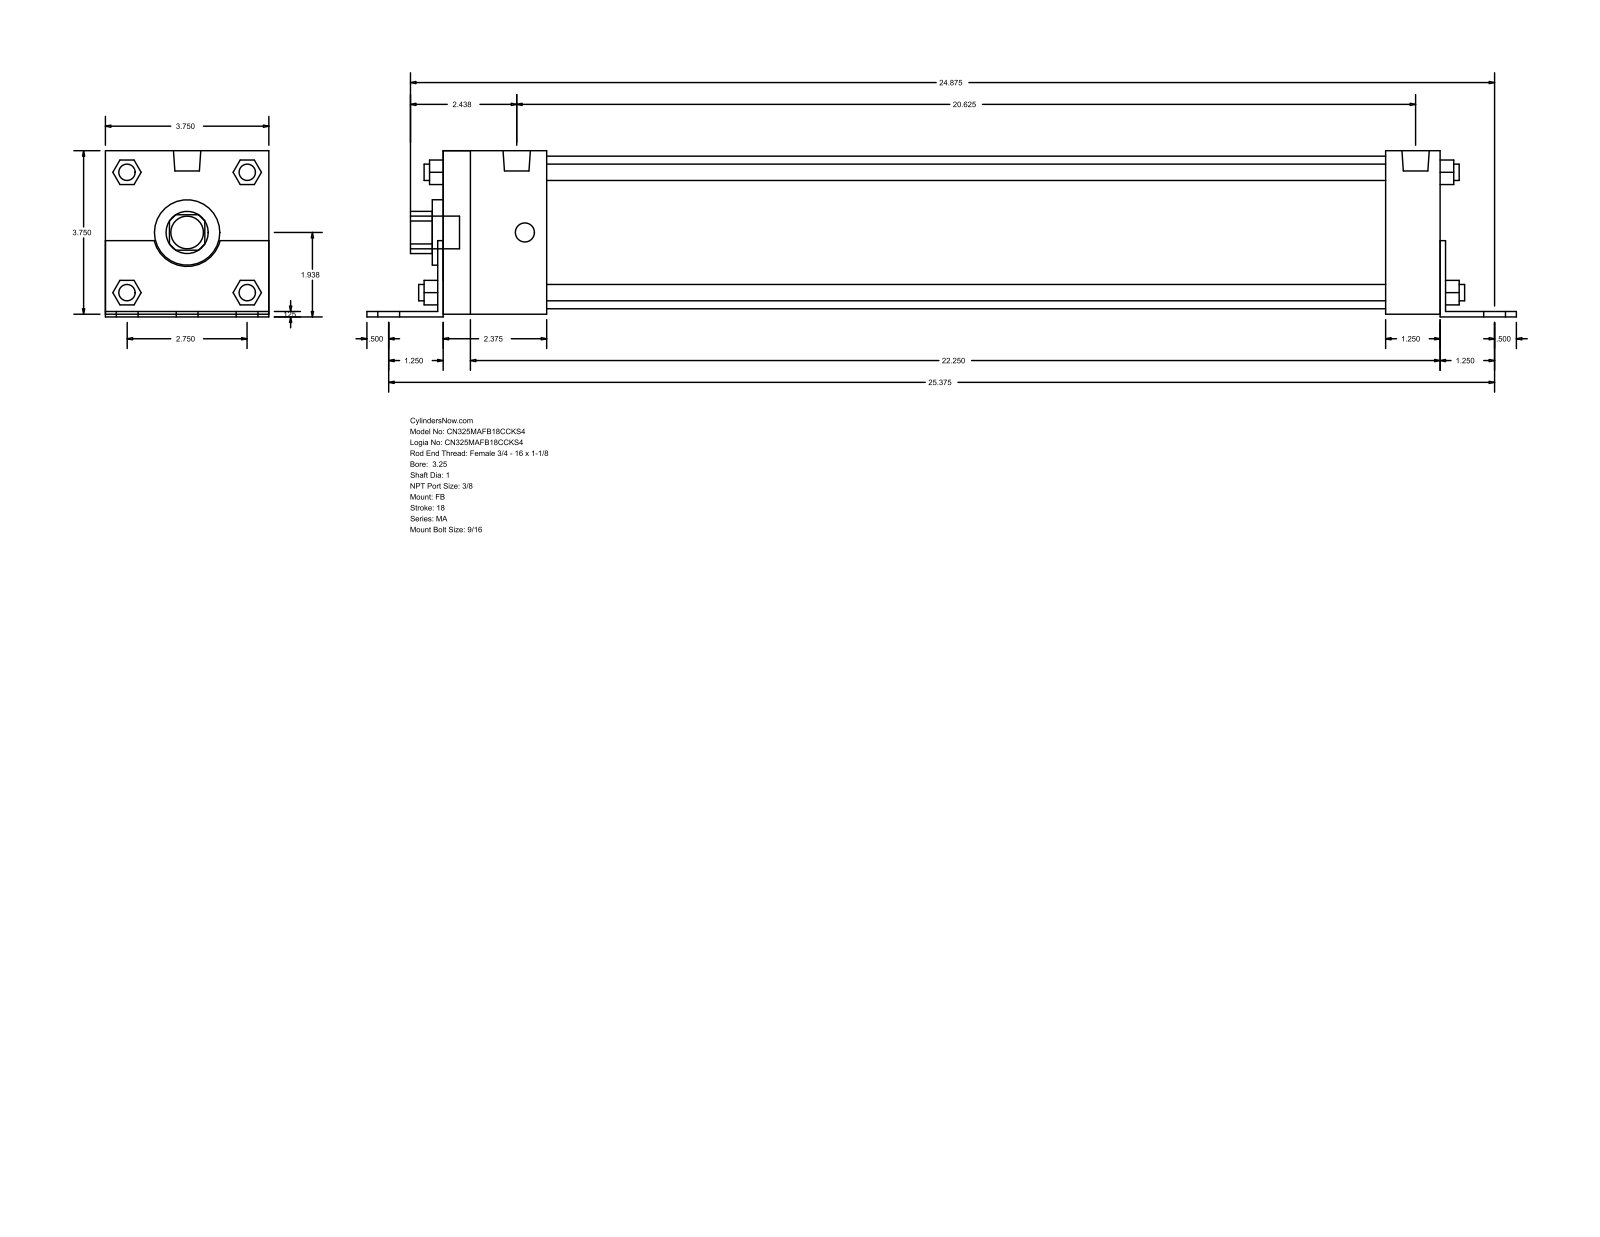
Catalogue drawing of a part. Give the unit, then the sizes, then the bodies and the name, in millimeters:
Units: millimetres
Overall size (bounding box): 669.92 × 96.84 × 95.25
Round holes (diameter × count): ⌀25.4 ×1, ⌀38.1 ×1, ⌀88.9 ×1
Round bosses / shafts (diameter × count): ⌀14.29 ×6, ⌀11.11 ×4, ⌀9.53 ×4, ⌀15.93 ×2, ⌀19.05 ×1
Partial cylindrical surfaces — rounded edges, fillets, slot ends (radius × count): R12.29 ×1, R19.81 ×1
Main face-to-face distances: 95.24, 3.17, 1.59, 96.83, 1.58, 93.66, 584.2, 581.03, 587.37, 552.45
Bodies: 0 solids, 140 faces (105 planar, 35 cylindrical, 0 other)
Part name (STEP PRODUCT): MA_FB__0325_1
STEP written by: GSSL Pune (CONFIG_CONTROL_DESIGN)
